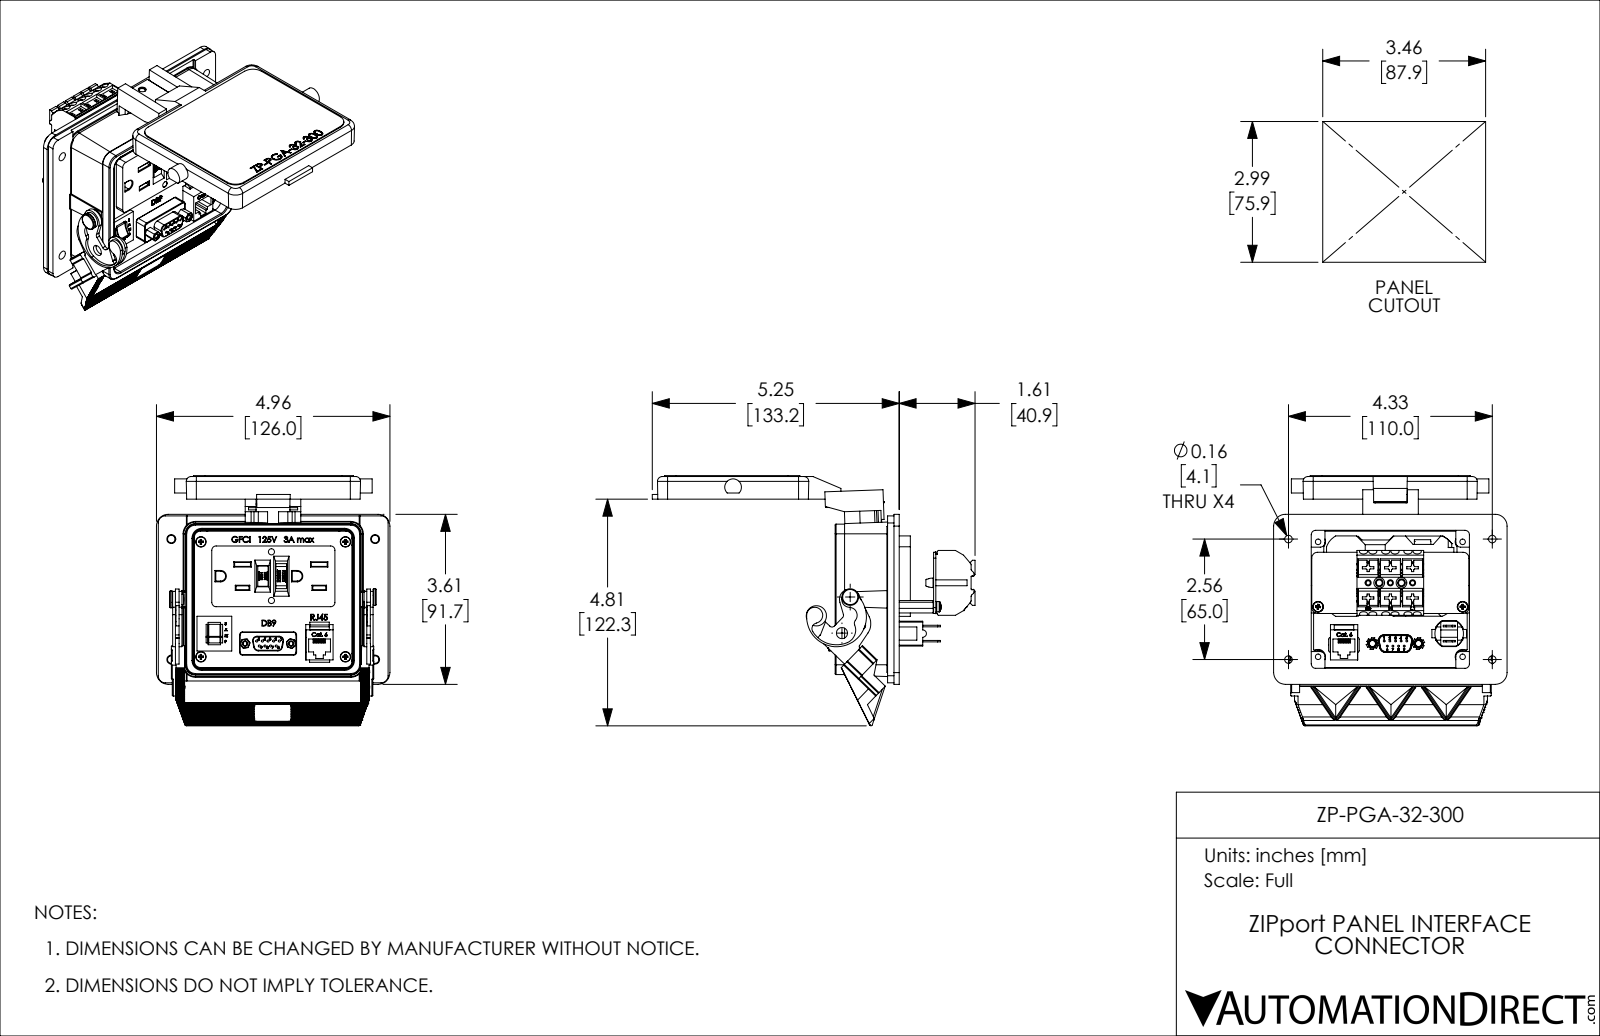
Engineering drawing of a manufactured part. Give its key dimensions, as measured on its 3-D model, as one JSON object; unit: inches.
{"part_name": "ZP-PGA-32-300", "step_written_by": "SolidWorks 2017 (AUTOMOTIVE_DESIGN)", "units": "inches", "bodies": {"solids": 1, "faces": 3854, "planar": 2465, "cylindrical": 714, "other": 675}, "overall_size": [6.857, 5.313, 4.96], "volume_in3": 16.67, "surface_area_in2": 198.5, "round_holes": [[0.045, 9], [0.144, 8], [0.13, 6], [0.138, 6], [0.173, 6], [0.098, 4], [0.16, 4], [0.175, 4], [0.19, 4], [0.091, 3], [0.09, 2], [0.097, 2]], "round_bosses_or_shafts": [[0.038, 9], [0.22, 6], [0.118, 6], [0.315, 4], [0.205, 3], [0.354, 2], [0.226, 2], [0.109, 2]], "partial_cylinders_radius": [[0.02, 26], [0.1, 18], [0.015, 13], [0.025, 12], [0.125, 12], [0.25, 12], [0.005, 8], [0.012, 8]], "face_to_face_distances": [0.135, 0.06, 1.015, 0.954, 0.73, 1.685, 1.745, 1.19, 0.495, 0.235], "hole_center_spacings": [0.12, 0.472, 0.633, 0.236, 0.24, 1.063, 1.287, 1.378]}
